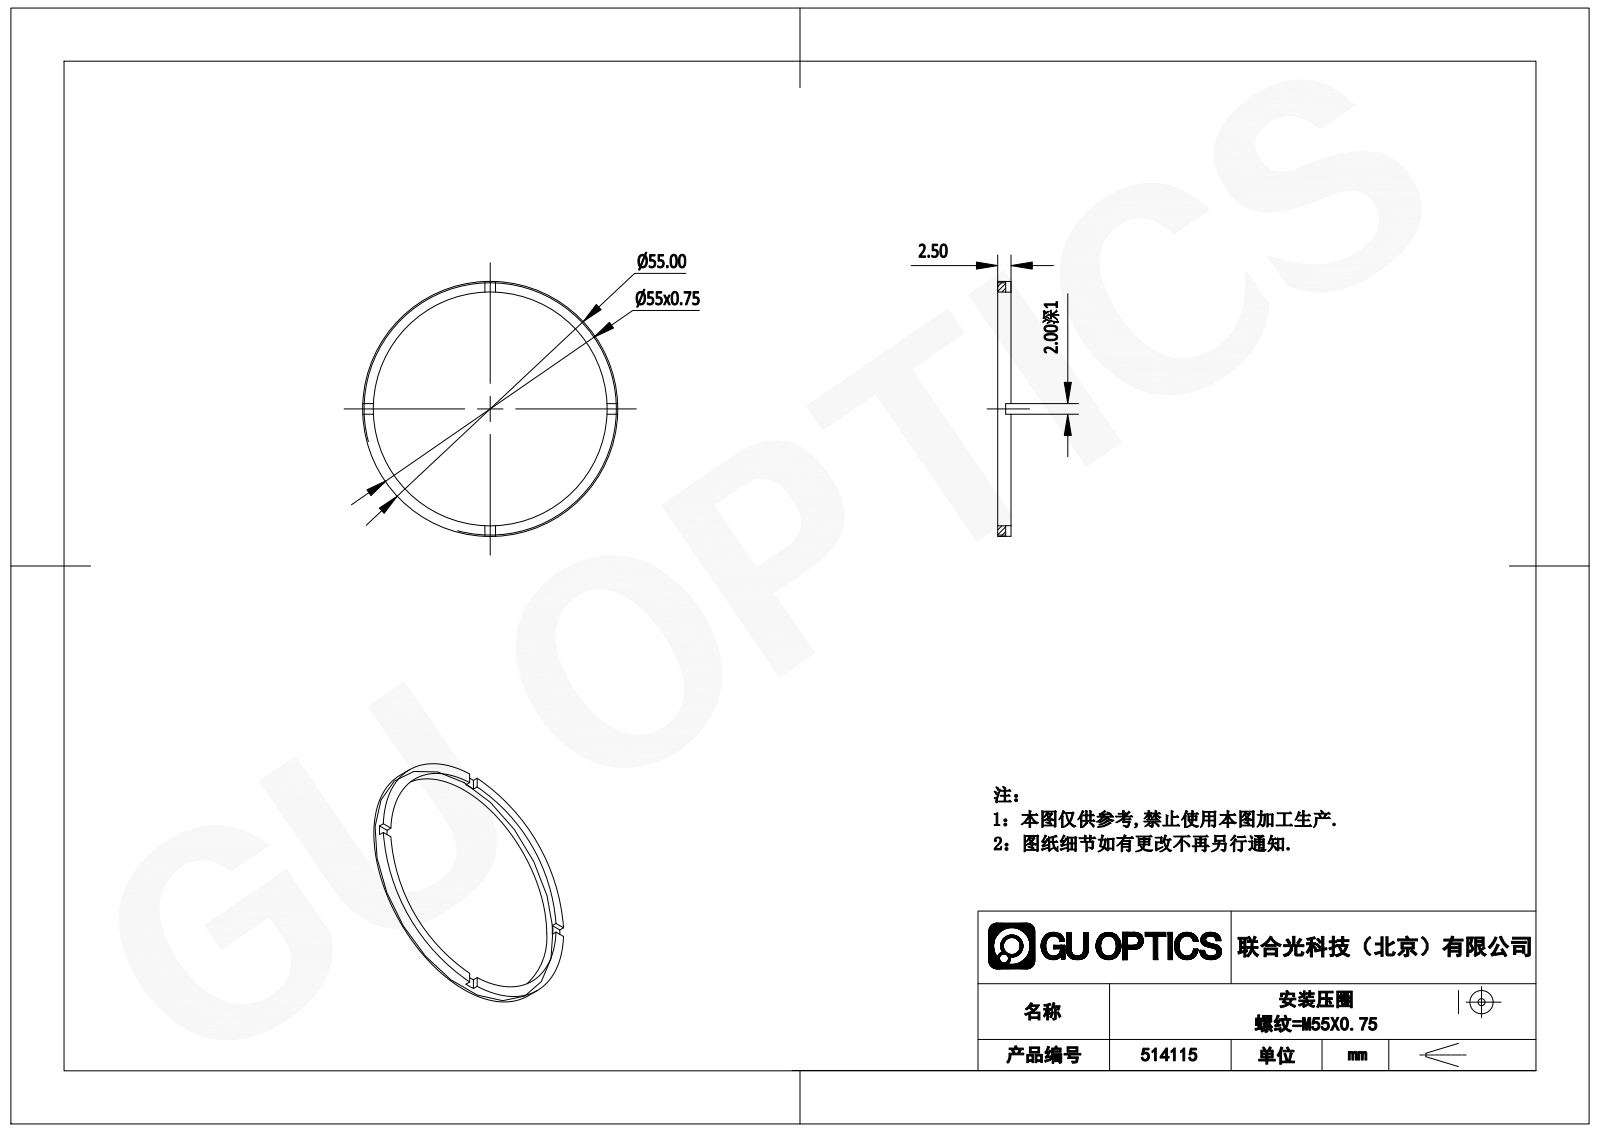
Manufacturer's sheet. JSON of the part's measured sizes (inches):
{"part_name": "514115", "step_written_by": "SolidWorks 2020 (CONFIG_CONTROL_DESIGN)", "units": "inches", "bodies": {"solids": 1, "faces": 21, "planar": 17, "cylindrical": 4, "other": 0}, "overall_size": [2.165, 2.165, 0.098], "volume_in3": 0.062, "surface_area_in2": 2.562, "round_holes": [[1.969, 1]], "round_bosses_or_shafts": [[2.165, 1]], "face_to_face_distances": [0.098, 0.059, 0.039, 0.079]}
